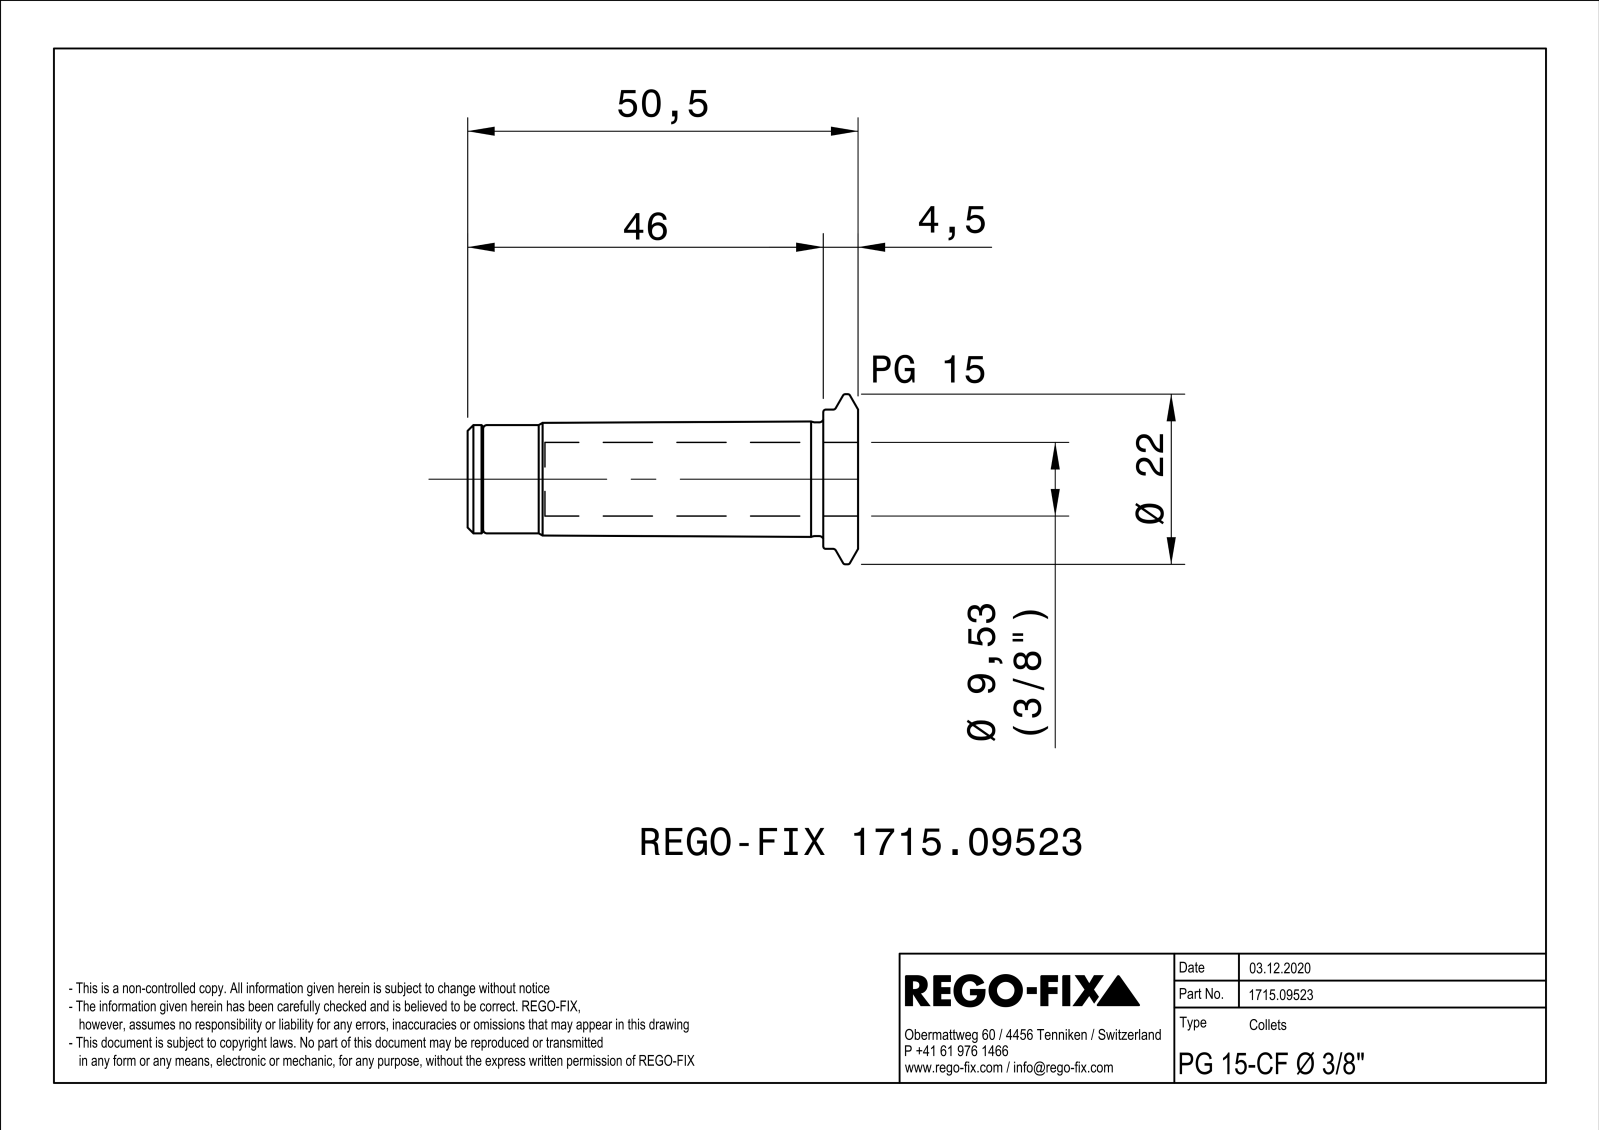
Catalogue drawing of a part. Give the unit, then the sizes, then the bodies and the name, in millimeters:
Units: millimetres
Overall size (bounding box): 50.5 × 22 × 21.99
Round holes (diameter × count): ⌀5.2 ×1, ⌀6.92 ×1, ⌀8.2 ×1, ⌀9.53 ×1, ⌀10.92 ×1, ⌀12.2 ×1
Round bosses / shafts (diameter × count): ⌀22 ×1, ⌀18 ×1, ⌀14.7 ×1, ⌀14 ×1
Partial cylindrical surfaces — rounded edges, fillets, slot ends (radius × count): R0.5 ×3, R5.2 ×1, R6 ×1
Main face-to-face distances: 1, 2, 50.5, 40.5, 10, 41.5, 9, 3, 4.5, 36
Volume: 5 277 mm³ · Surface area: 5 362 mm²
Bodies: 1 solid, 120 faces (41 planar, 30 cylindrical, 49 other)
Part name (STEP PRODUCT): NOCUT
STEP written by: SIEMENS PLM Software Solid Edge ST10 (AUTOMOTIVE_DESIGN)
